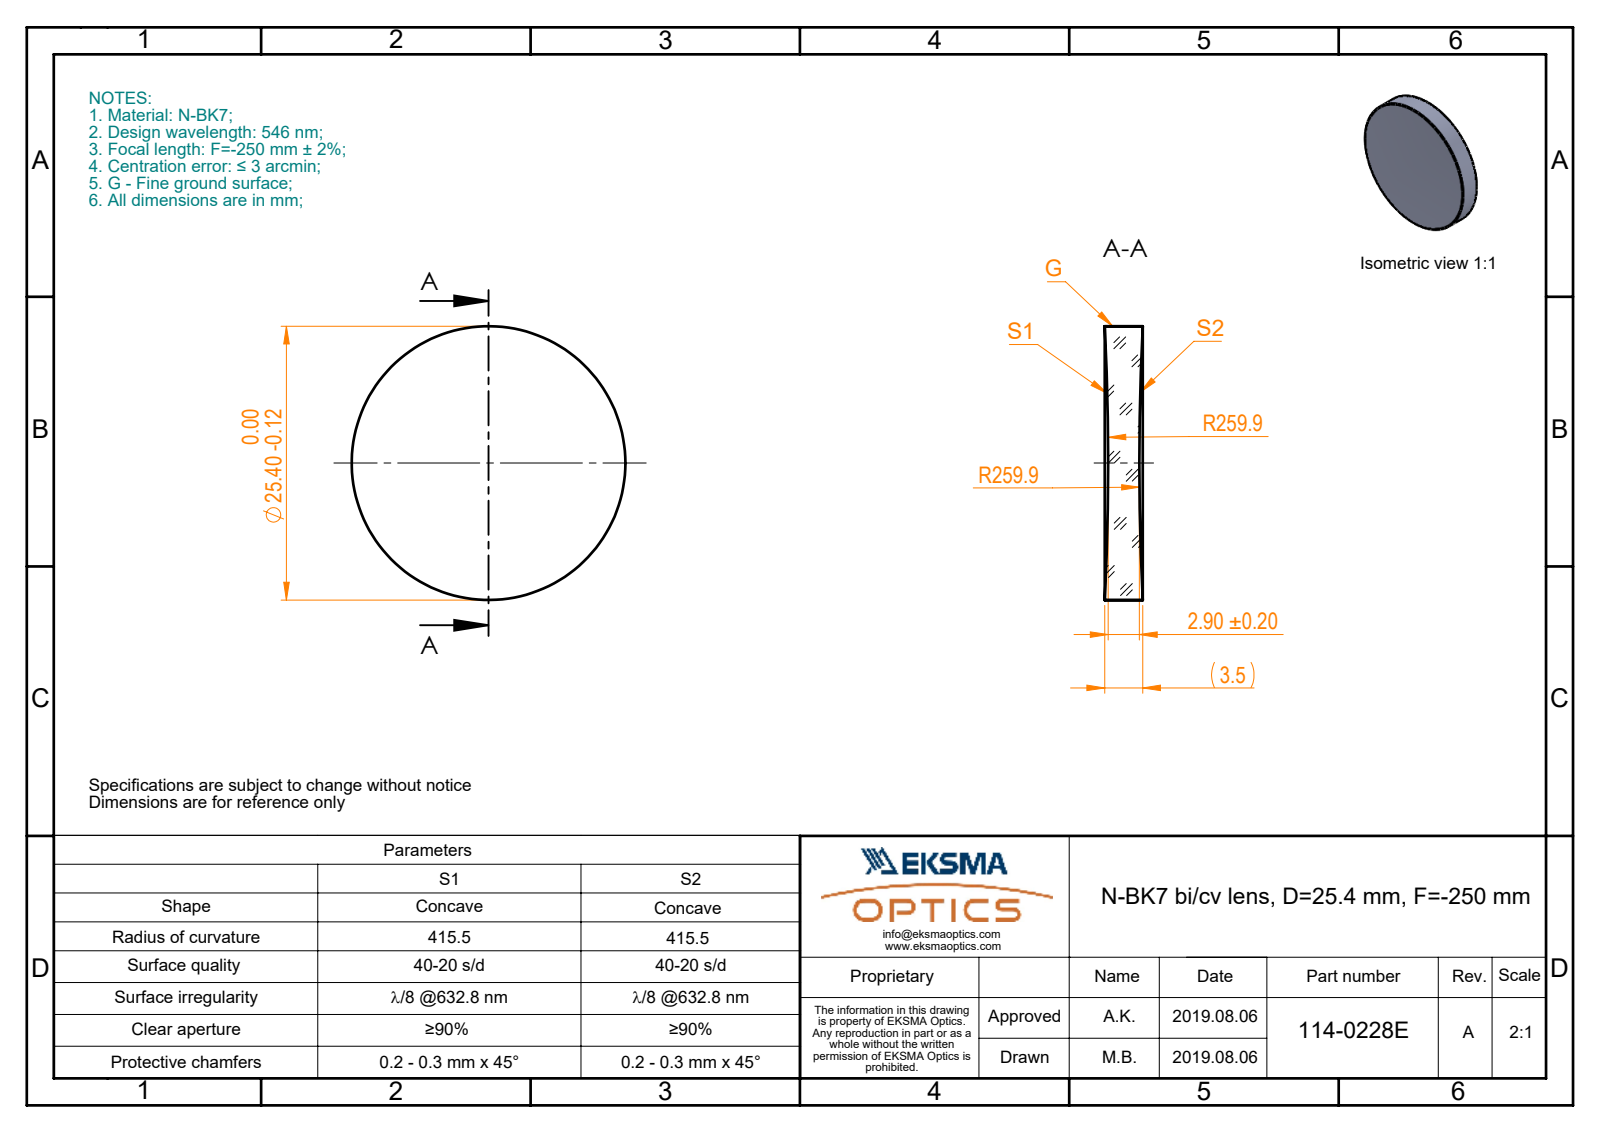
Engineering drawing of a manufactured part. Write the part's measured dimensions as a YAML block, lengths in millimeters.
part_name: "114-0228E BK7 bi-cv 25.4 F-250"
step_written_by: "SolidWorks 2017 (CONFIG_CONTROL_DESIGN)"
units: millimeters
bodies: {solids: 1, faces: 6, planar: 0, cylindrical: 2, other: 4}
overall_size: [25.4, 25.4, 3.52]
volume: 1627
surface_area: 1295
round_bosses_or_shafts:
  - {diameter: 25.4, count: 1}
